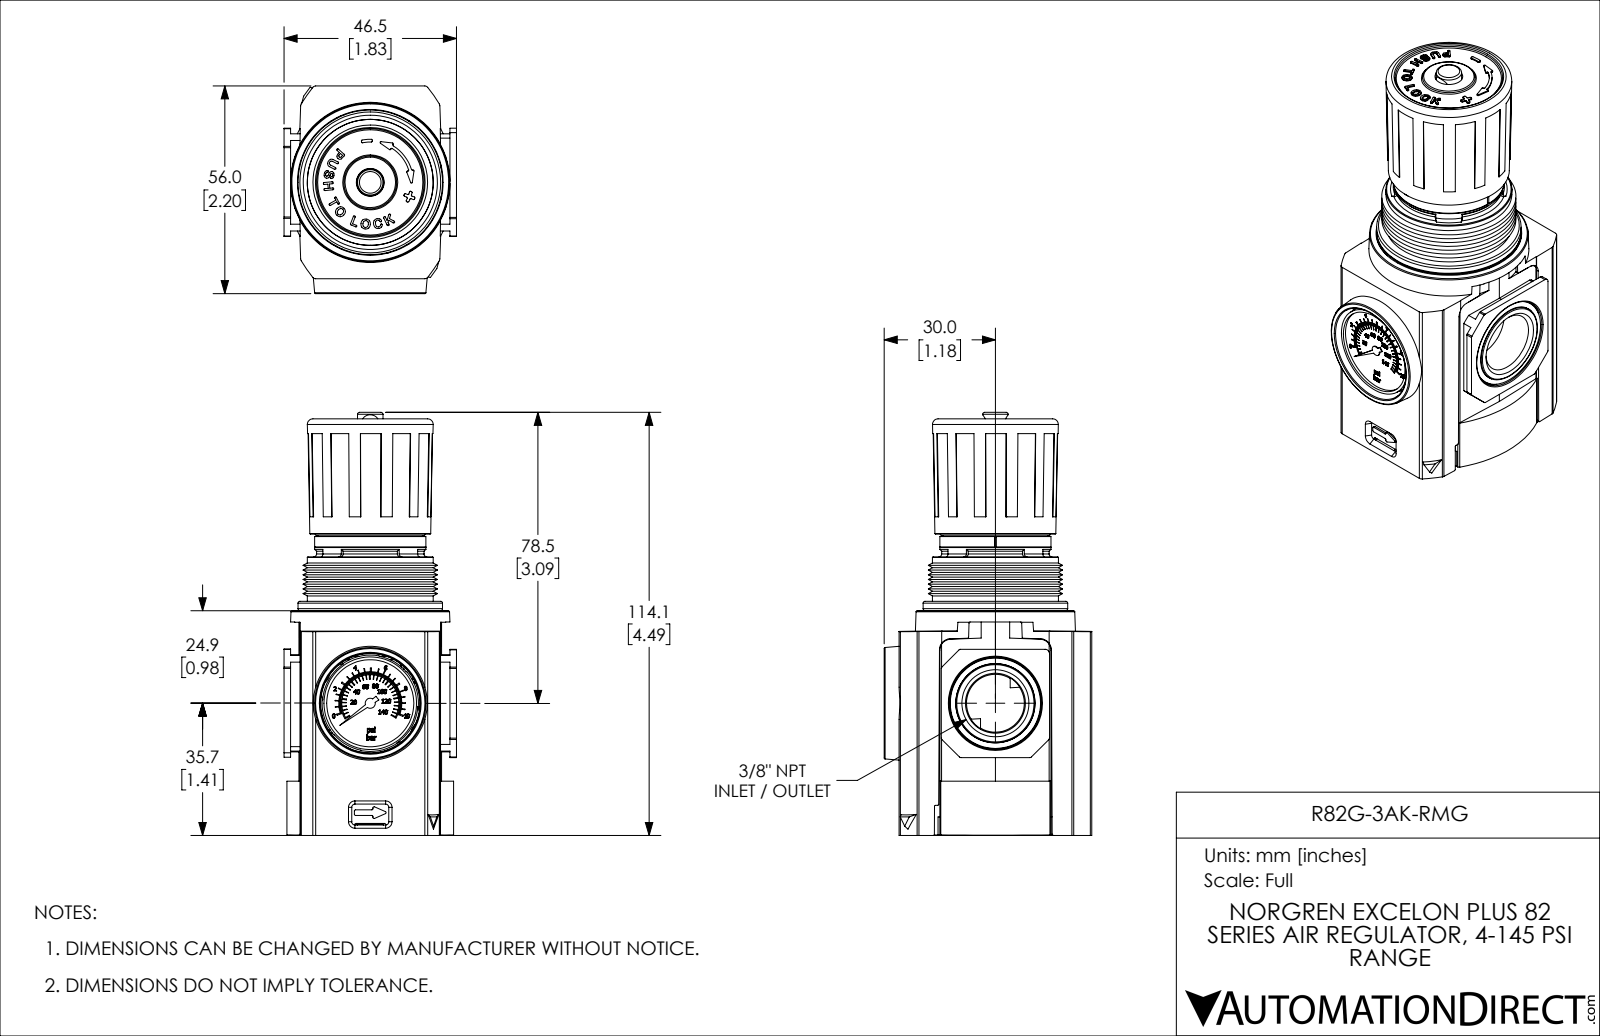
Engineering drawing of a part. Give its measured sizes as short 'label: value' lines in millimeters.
name: R82G-3AK-RMG
written by: SolidWorks 2021 (CONFIG_CONTROL_DESIGN)
unit: mm
bodies: 5 solids, 2163 faces (770 planar, 1066 cylindrical, 327 other)
size: 114.1 × 56 × 46.5
volume: 144 900 mm³; area: 56 170 mm²
holes: 4× ⌀2.5, 2× ⌀3.5, 1× ⌀3.3, 1× ⌀5, 1× ⌀6, 1× ⌀22.5, 1× ⌀23.5, 1× ⌀28, 1× ⌀34.4
bosses: 2× ⌀5.7, 2× ⌀3, 1× ⌀39, 1× ⌀34, 1× ⌀30, 1× ⌀29.5, 1× ⌀28.9, 1× ⌀27.9
rounds: 68× R1, 39× R0.5, 25× R0.2, 20× R0.8, 12× R0.2, 12× R0.3, 12× R0.3, 12× R0.8
face distances: 1.5, 50.5, 4.6, 34.3, 9, 36, 37.5, 3.1, 32.8, 29.7
hole spacings: 16, 27.7, 32, 68.7, 84.5, 75.3
